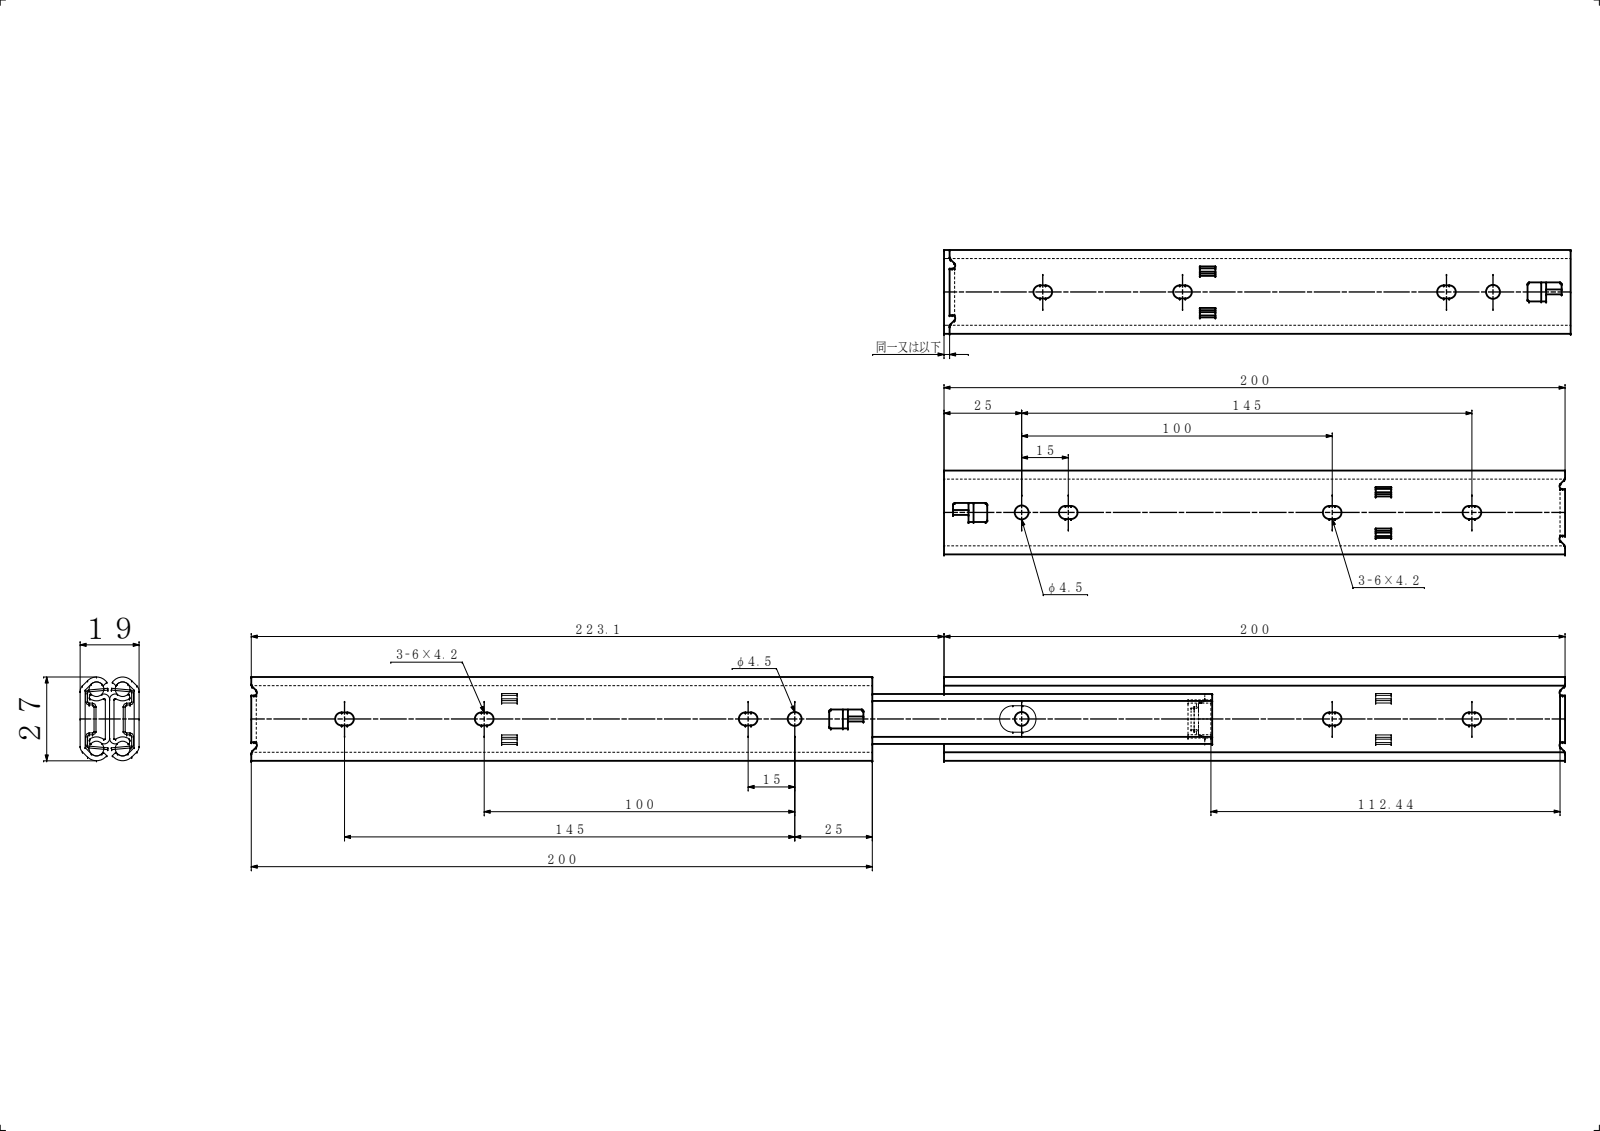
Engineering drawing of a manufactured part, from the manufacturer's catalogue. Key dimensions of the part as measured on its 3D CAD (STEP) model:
Part name (STEP PRODUCT): 2731MC-200 AS; OM-2731MC-200; IM-2731MC-200; SBP1015 (+1 more)
STEP written by: SolidWorks 2019 (CONFIG_CONTROL_DESIGN)
Units: millimetres
Bodies: 8 solids, 398 faces (200 planar, 178 cylindrical, 20 other)
Overall size (bounding box): 423.08 × 27 × 19.1
Volume: 38 400 mm³ · Surface area: 54 109 mm²
Round holes (diameter × count): ⌀4.5 ×2
Partial cylindrical surfaces — rounded edges, fillets, slot ends (radius × count): R1 ×38, R2 ×22, R0.1 ×16, R2.1 ×12, R0.3 ×8, R0.5 ×8, R2.38 ×8, R0.28 ×4
Main face-to-face distances: 1.6, 7.95, 9.55, 17.5, 1.4, 8.15, 10.95, 6.55, 9.35, 15.9
Hole centre spacings: 73.08
